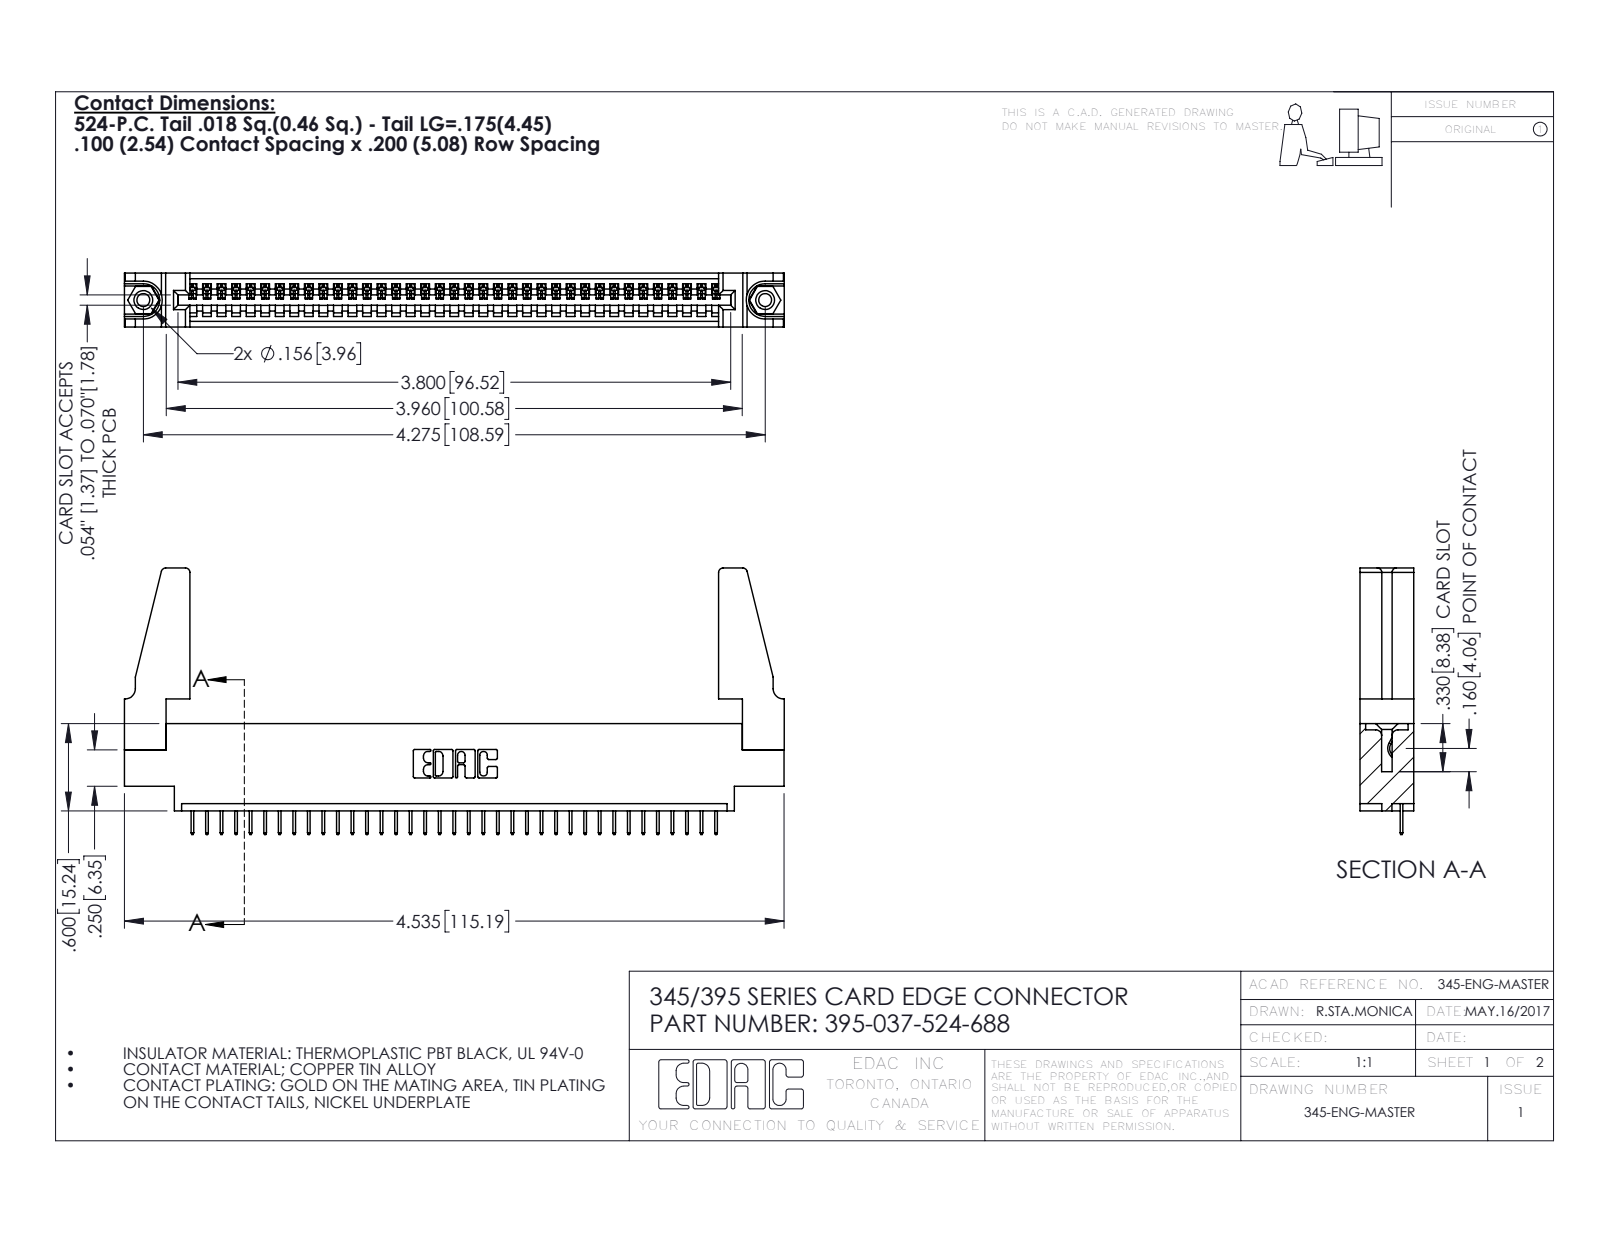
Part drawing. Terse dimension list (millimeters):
name: 395-037-524-688; 345-292-001_345-293-124; 345-250-001_345-250-001-102; 345 Part_0.170 Offset - 0.156 Dia-TH (+1 more)
written by: SolidWorks 2016 (CONFIG_CONTROL_DESIGN)
unit: mm
bodies: 42 solids, 2548 faces (1858 planar, 674 cylindrical, 16 other)
size: 115.2 × 46.5 × 9.4
volume: 13 900 mm³; area: 16 860 mm²
holes: 2× ⌀2.3, 2× ⌀3.2, 2× ⌀4, 1× ⌀1.6
bosses: 2× ⌀3.9
rounds: 74× R0.2, 22× R0.3, 8× R0.8, 6× R0.2, 6× R0.8, 3× R0.7, 2× R0.8, 2× R1
face distances: 9.4, 1.8, 7.6, 2.5, 6.9, 0.6, 5.1, 5.7, 1.8, 4.4
hole spacings: 6.9, 102.6, 108.6
